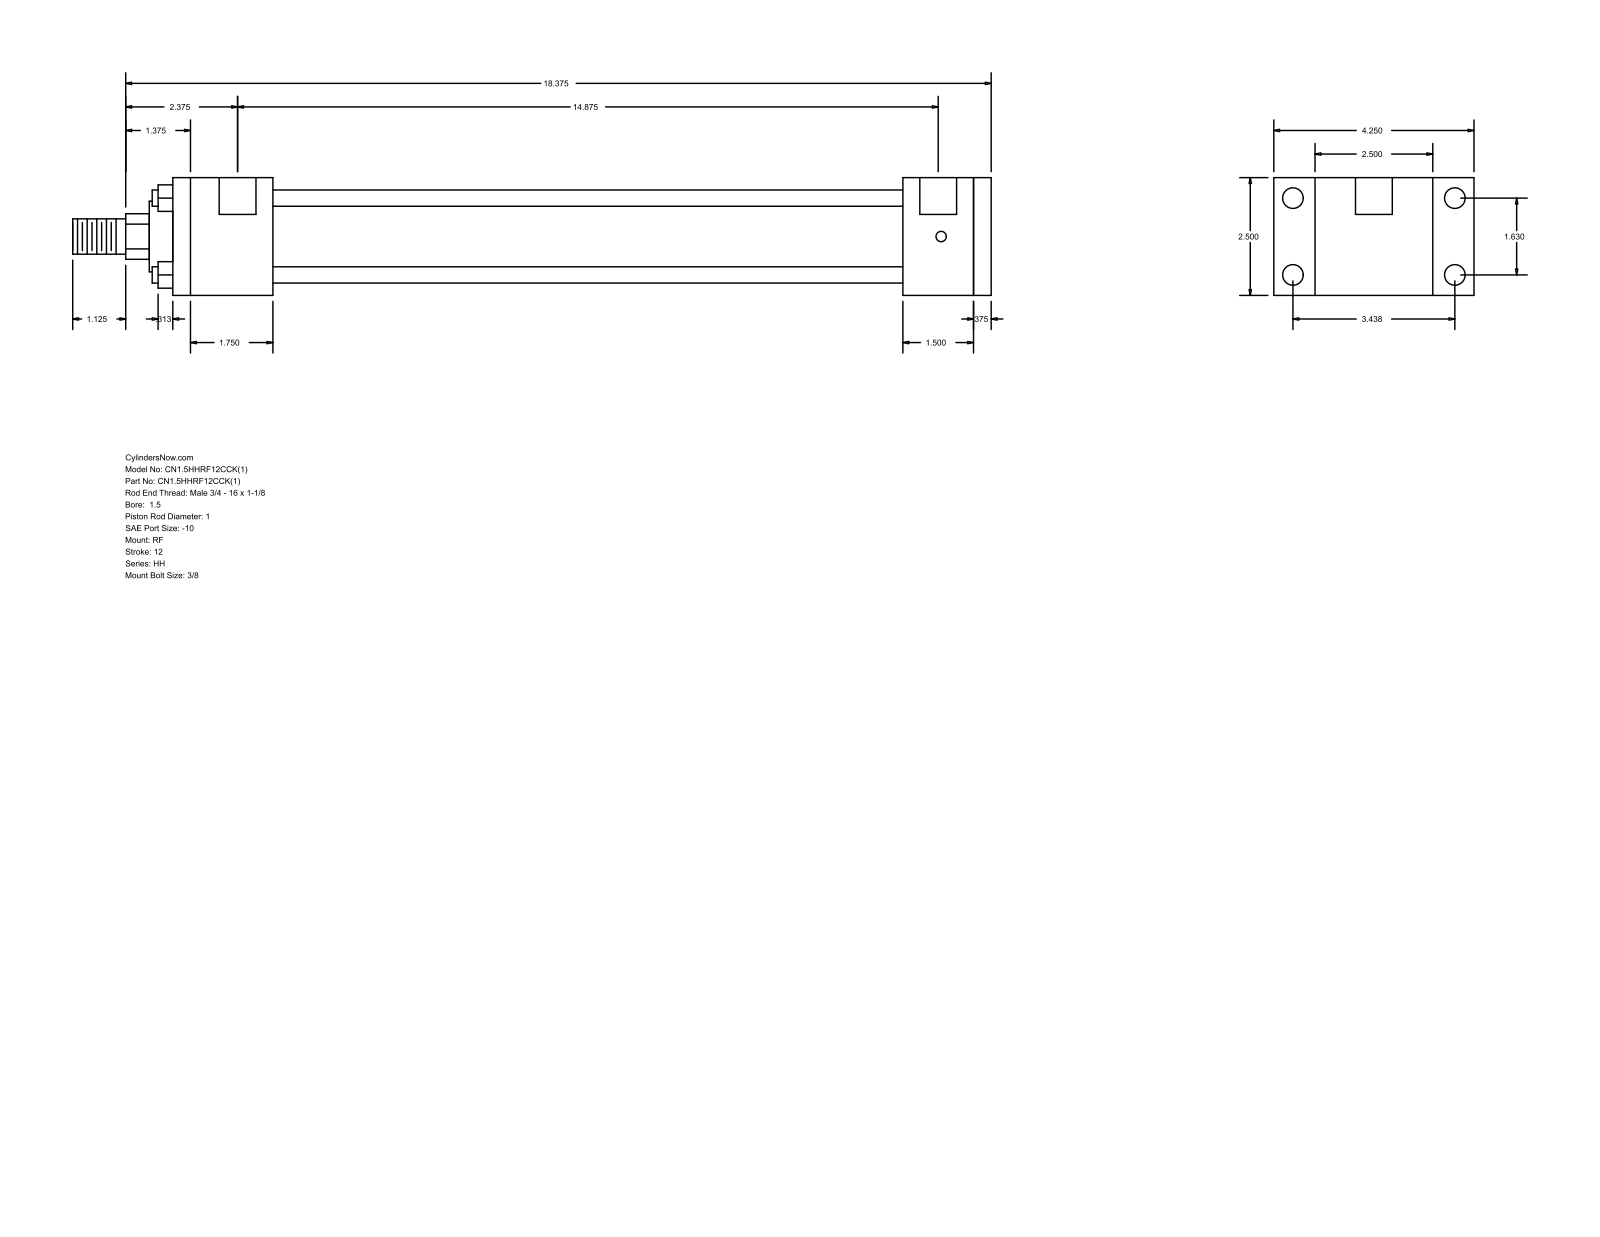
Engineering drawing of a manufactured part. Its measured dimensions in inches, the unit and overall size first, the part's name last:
Units: inches
Overall size (bounding box): 19.5 × 4.25 × 2.5
Round holes (diameter × count): ⌀0.219 ×4, ⌀0.438 ×4, ⌀0.781 ×2
Round bosses / shafts (diameter × count): ⌀0.345 ×4, ⌀1.75 ×1, ⌀1.5 ×1, ⌀1 ×1, ⌀0.75 ×1
Partial cylindrical surfaces — rounded edges, fillets, slot ends (radius × count): R0.484 ×1
Main face-to-face distances: 2.5, 0.375, 1.5, 13.375, 14.875, 15.25, 1.875, 2.125, 15.5, 17
Hole centre spacings: 0.063, 1.63, 3.438, 3.805, 14.937, 15, 14.875
Bodies: 0 solids, 92 faces (64 planar, 28 cylindrical, 0 other)
Part name (STEP PRODUCT): HH_RF__0150_1
STEP written by: GSSL Pune (CONFIG_CONTROL_DESIGN)
